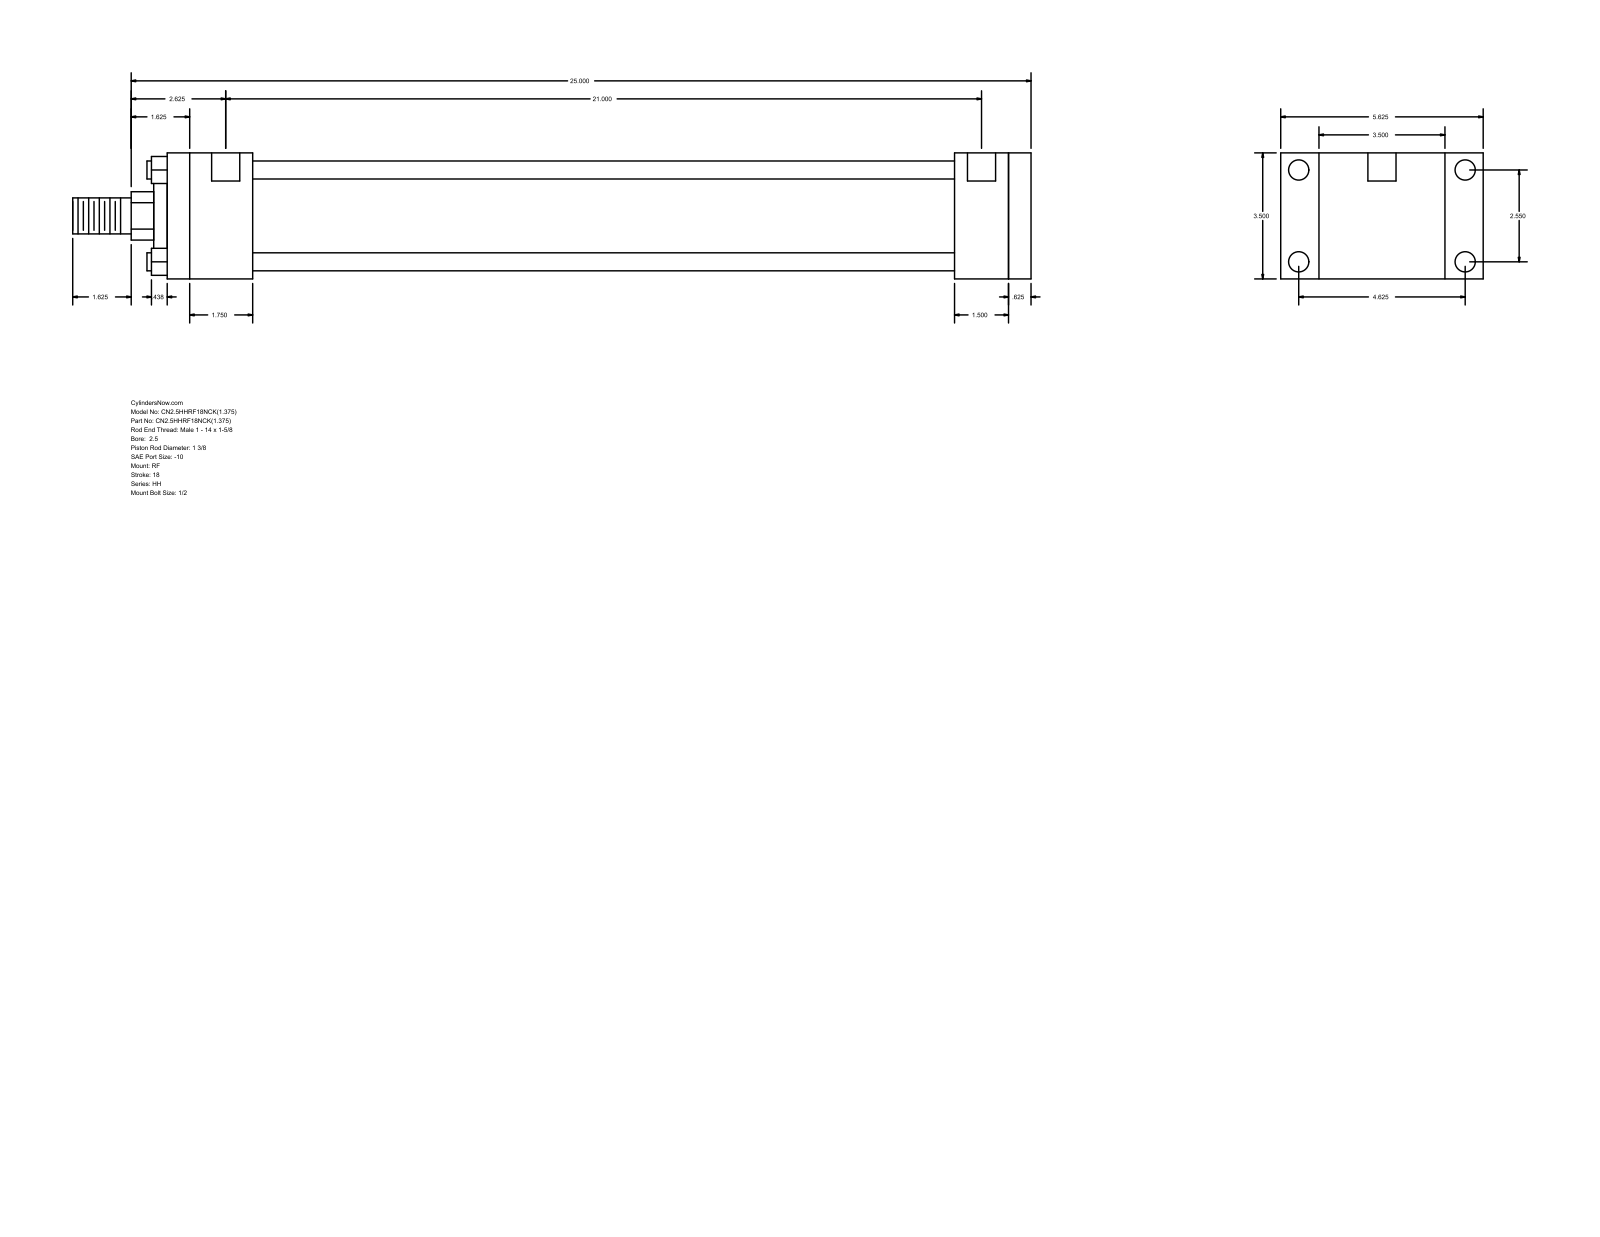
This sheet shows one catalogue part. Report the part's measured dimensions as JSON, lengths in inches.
{"part_name": "HH_RF__0250_1.375", "step_written_by": "GSSL Pune (CONFIG_CONTROL_DESIGN)", "units": "inches", "bodies": {"solids": 0, "faces": 92, "planar": 64, "cylindrical": 28, "other": 0}, "overall_size": [26.625, 5.625, 3.5], "round_holes": [[0.219, 4], [0.563, 4], [0.781, 2]], "round_bosses_or_shafts": [[0.5, 4], [2.875, 1], [2, 1], [1.375, 1], [1, 1]], "partial_cylinders_radius": [[0.672, 1]], "face_to_face_distances": [3.5, 24, 0.625, 23.375, 2.375, 21, 21.625, 21.875, 19.5, 1.5], "hole_center_spacings": [0.062, 2.55, 4.625, 5.281, 21.063, 21.125, 21]}
